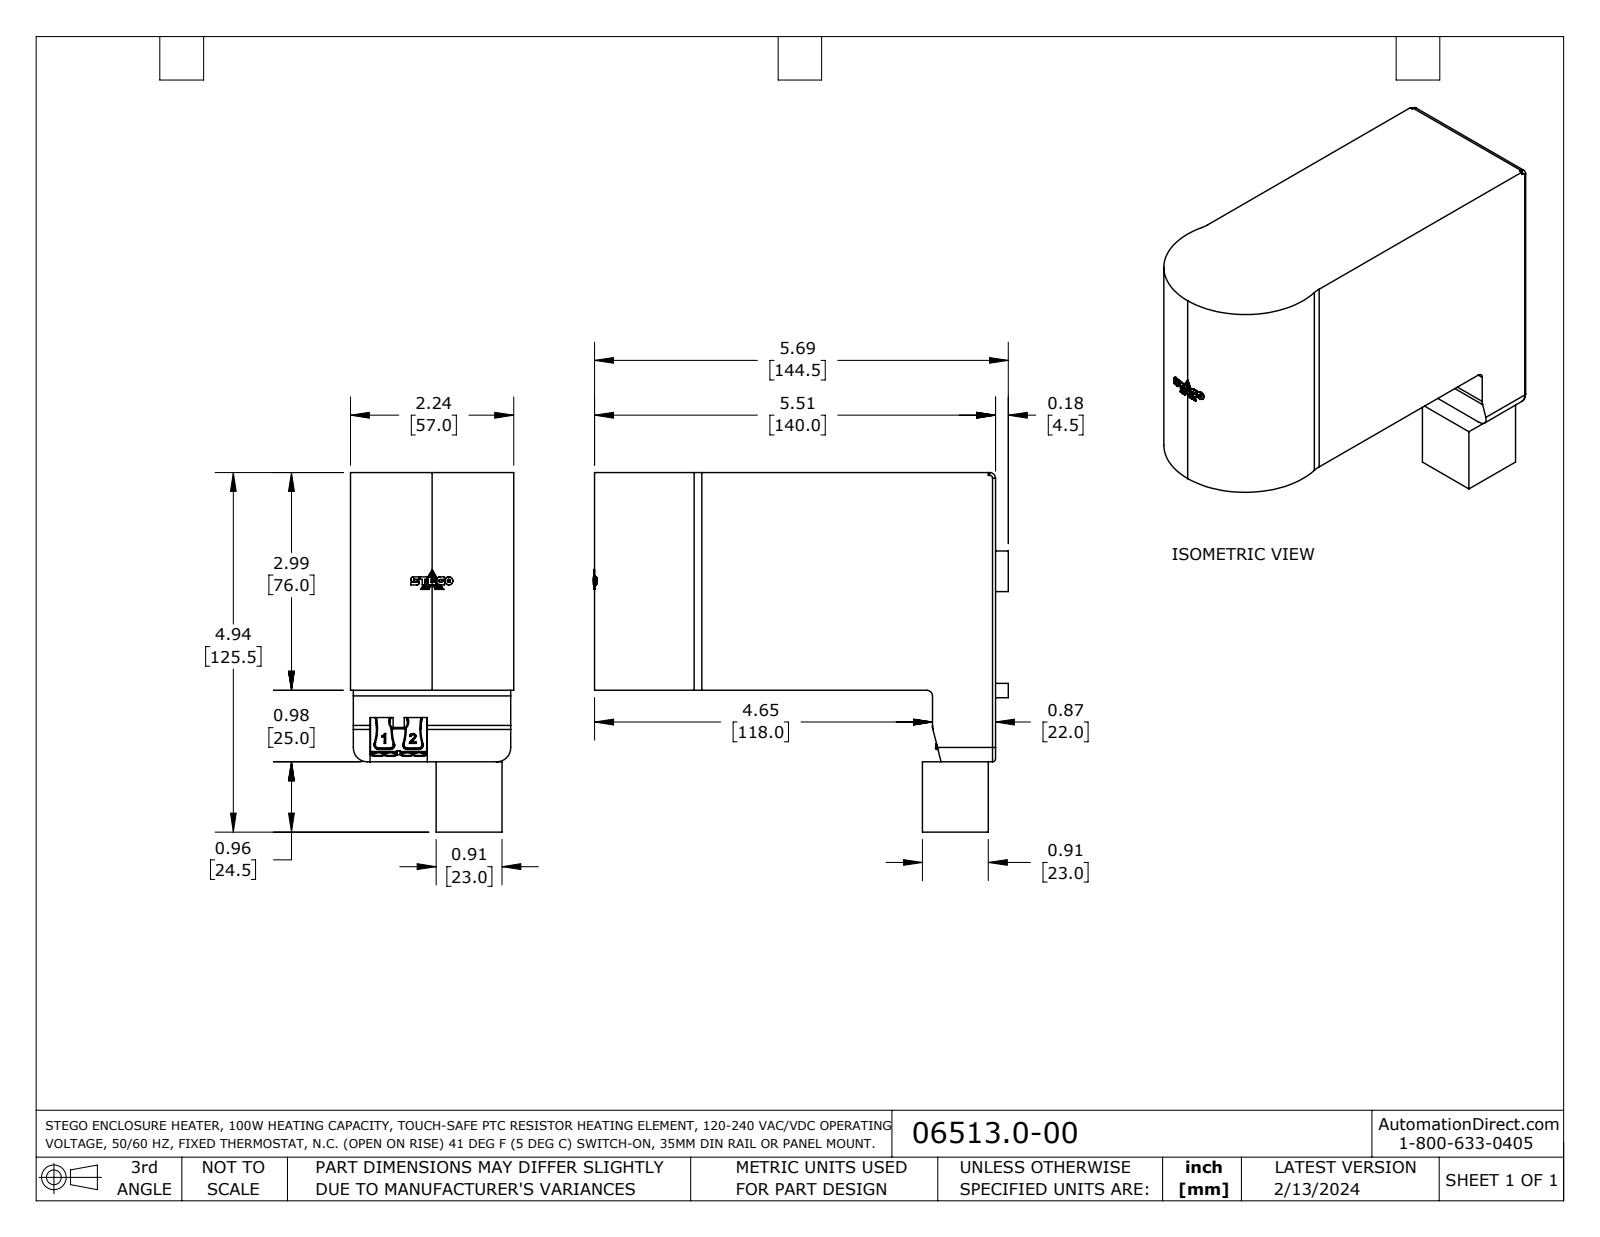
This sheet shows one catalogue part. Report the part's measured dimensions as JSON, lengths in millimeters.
{"part_name": "06513.0-00", "step_written_by": "SolidWorks 2023 (AUTOMOTIVE_DESIGN)", "units": "millimeters", "bodies": {"solids": 3, "faces": 628, "planar": 387, "cylindrical": 173, "other": 68}, "overall_size": [207, 140, 58.6], "volume_mm3": 1134000, "surface_area_mm2": 125400, "partial_cylinders_radius": [[1.8, 40], [1.7, 34], [1.6, 18], [1.1, 4], [2, 2], [7.2, 2], [26.5, 2], [4.7, 1]], "face_to_face_distances": [1.6, 2, 145.2, 57, 0.4, 143.6, 145.6, 143.2, 147.2, 144]}
